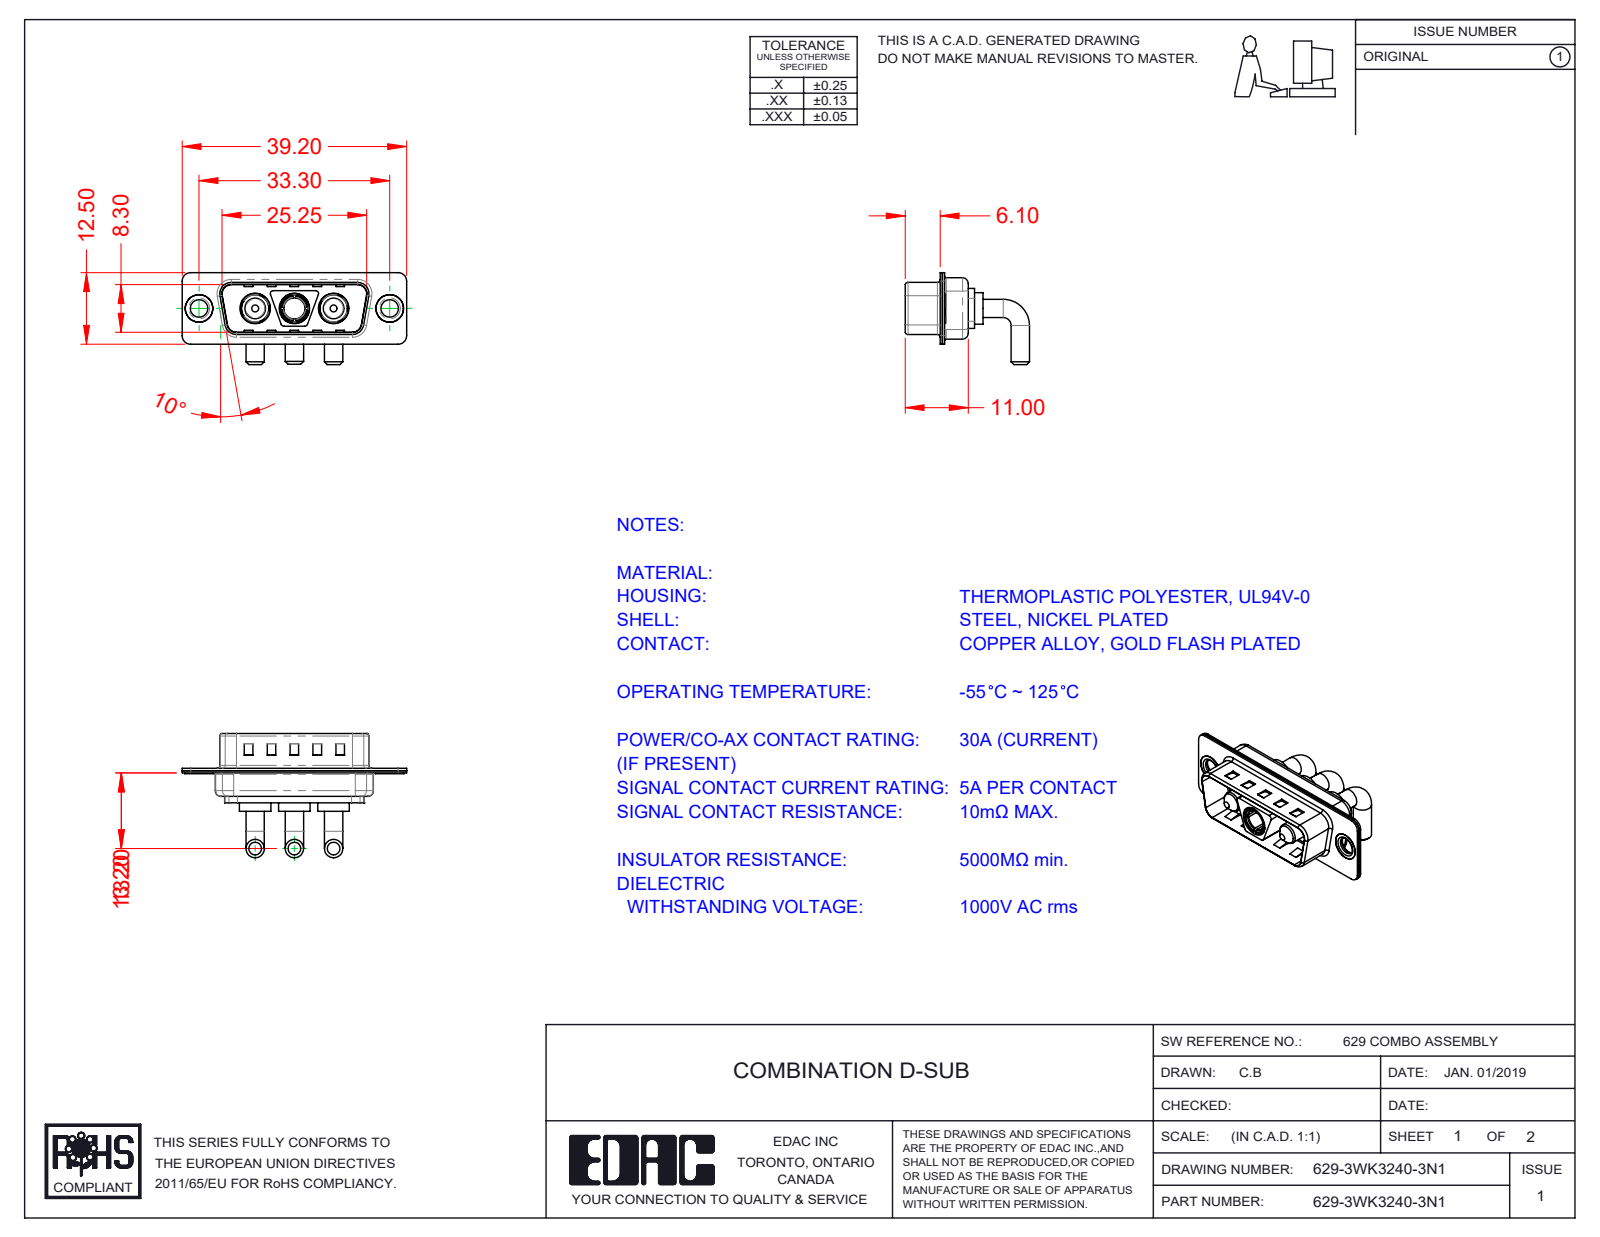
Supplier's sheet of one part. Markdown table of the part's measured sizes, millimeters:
| quantity | value |
| --- | --- |
| part name | Power Pin_30A RA; Power Socket_30A RA; 629Combo Shell Front_15 Contacts; 629Combo Thru Hole Rivet (+3 more) |
| STEP written by | SolidWorks 2020 (CONFIG_CONTROL_DESIGN) |
| units | millimeters |
| bodies | 11 solids, 488 faces (193 planar, 189 cylindrical, 106 other) |
| overall size | 39.2 × 21.7 × 16.05 |
| volume | 2 361 mm³ |
| surface area | 5 273 mm² |
| round holes (diameter × count) | 4.85 × 3, 5.3 × 3, 3.05 × 2, 4 × 2, 4.8 × 2, 3.7 × 1 |
| round bosses / shafts (diameter × count) | 3.2 × 6, 5.5 × 3, 5.2 × 3, 4.75 × 3, 3.75 × 3, 5 × 2, 4.9 × 2, 3.6 × 2 |
| partial cylindrical surfaces (radius × count) | 1.5 × 16, 0.5 × 12, 2 × 12, 1.6 × 8, 0.25 × 4, 0.6 × 4, 0.65 × 4, 0.9 × 4 |
| main face-to-face distances | 0.4, 0.8, 9.5, 9.1, 8.7, 9.9, 0.75, 1.2, 0.35, 6 |
| hole center spacings | 6.85, 9.8, 16.65, 23.5, 13.7, 33.3 |
